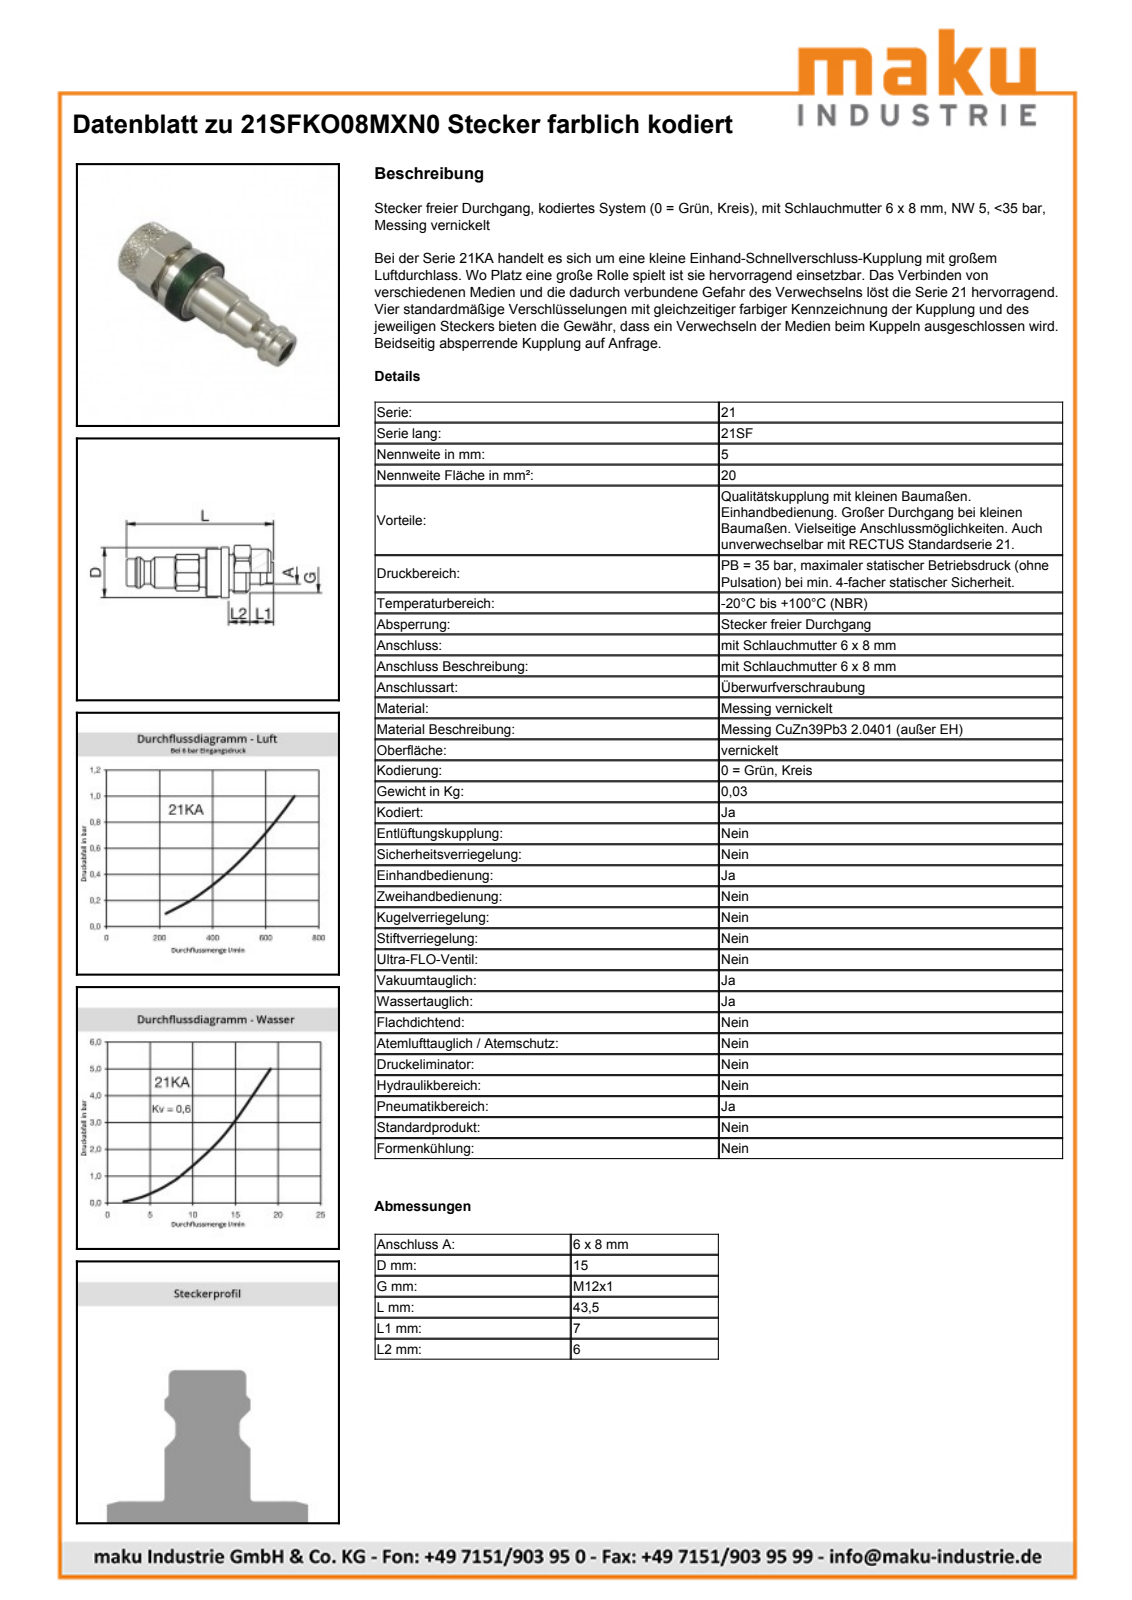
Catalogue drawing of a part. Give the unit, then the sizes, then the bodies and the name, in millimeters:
Units: millimetres
Overall size (bounding box): 43.5 × 15.5 × 15.5
Round holes (diameter × count): ⌀4.95 ×1, ⌀8.25 ×1, ⌀10 ×1, ⌀11.15 ×1, ⌀13.85 ×1, ⌀14.05 ×1
Round bosses / shafts (diameter × count): ⌀15.5 ×1, ⌀15 ×1, ⌀14 ×1, ⌀12 ×1, ⌀10.42 ×1, ⌀10.4 ×1, ⌀9 ×1, ⌀8.4 ×1
Main face-to-face distances: 14, 6.75, 2.25, 4.5, 13, 15.25, 19.75, 6.85, 6.15, 8.4
Volume: 3 552 mm³ · Surface area: 3 948 mm²
Bodies: 3 solids, 82 faces (18 planar, 26 cylindrical, 38 other)
Part name (STEP PRODUCT): D110428; D110427; D104771; D102231
STEP written by: Autodesk Inventor 2013 (AUTOMOTIVE_DESIGN)
